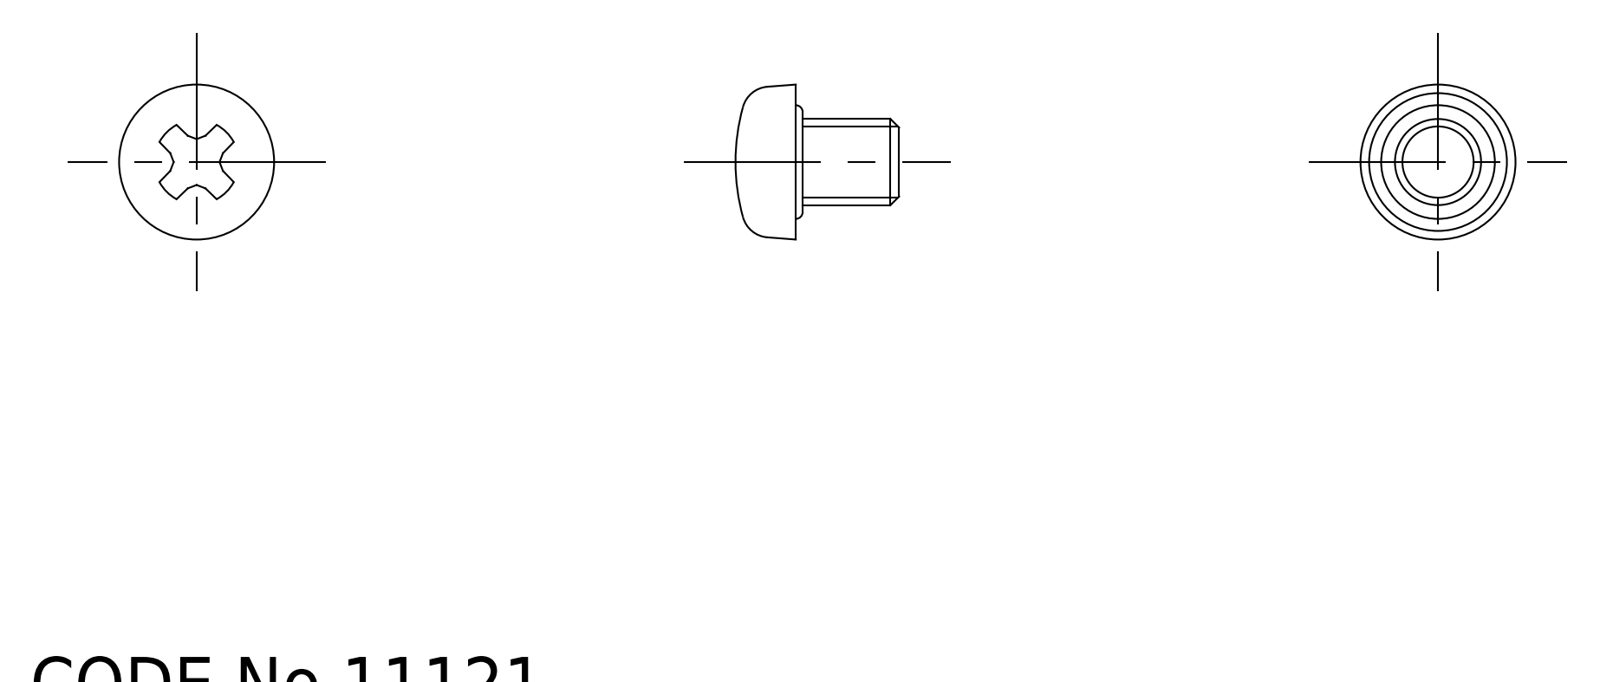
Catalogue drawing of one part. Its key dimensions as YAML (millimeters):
part_name: "TL_416_M5_6; screw"
step_written_by: "SolidWorks 2015 (AUTOMOTIVE_DESIGN)"
units: millimeters
bodies: {solids: 2, faces: 40, planar: 20, cylindrical: 8, other: 12}
overall_size: [9.43, 9, 9]
volume: 284
surface_area: 356
round_holes:
  - {diameter: 8, count: 1}
round_bosses_or_shafts:
  - {diameter: 5, count: 1}
partial_cylinders:
  - {radius: 2.45, count: 1}
face_to_face_distances: [2.5, 0.4, 6.4, 6, 2.1, 8.5, 1.5]
